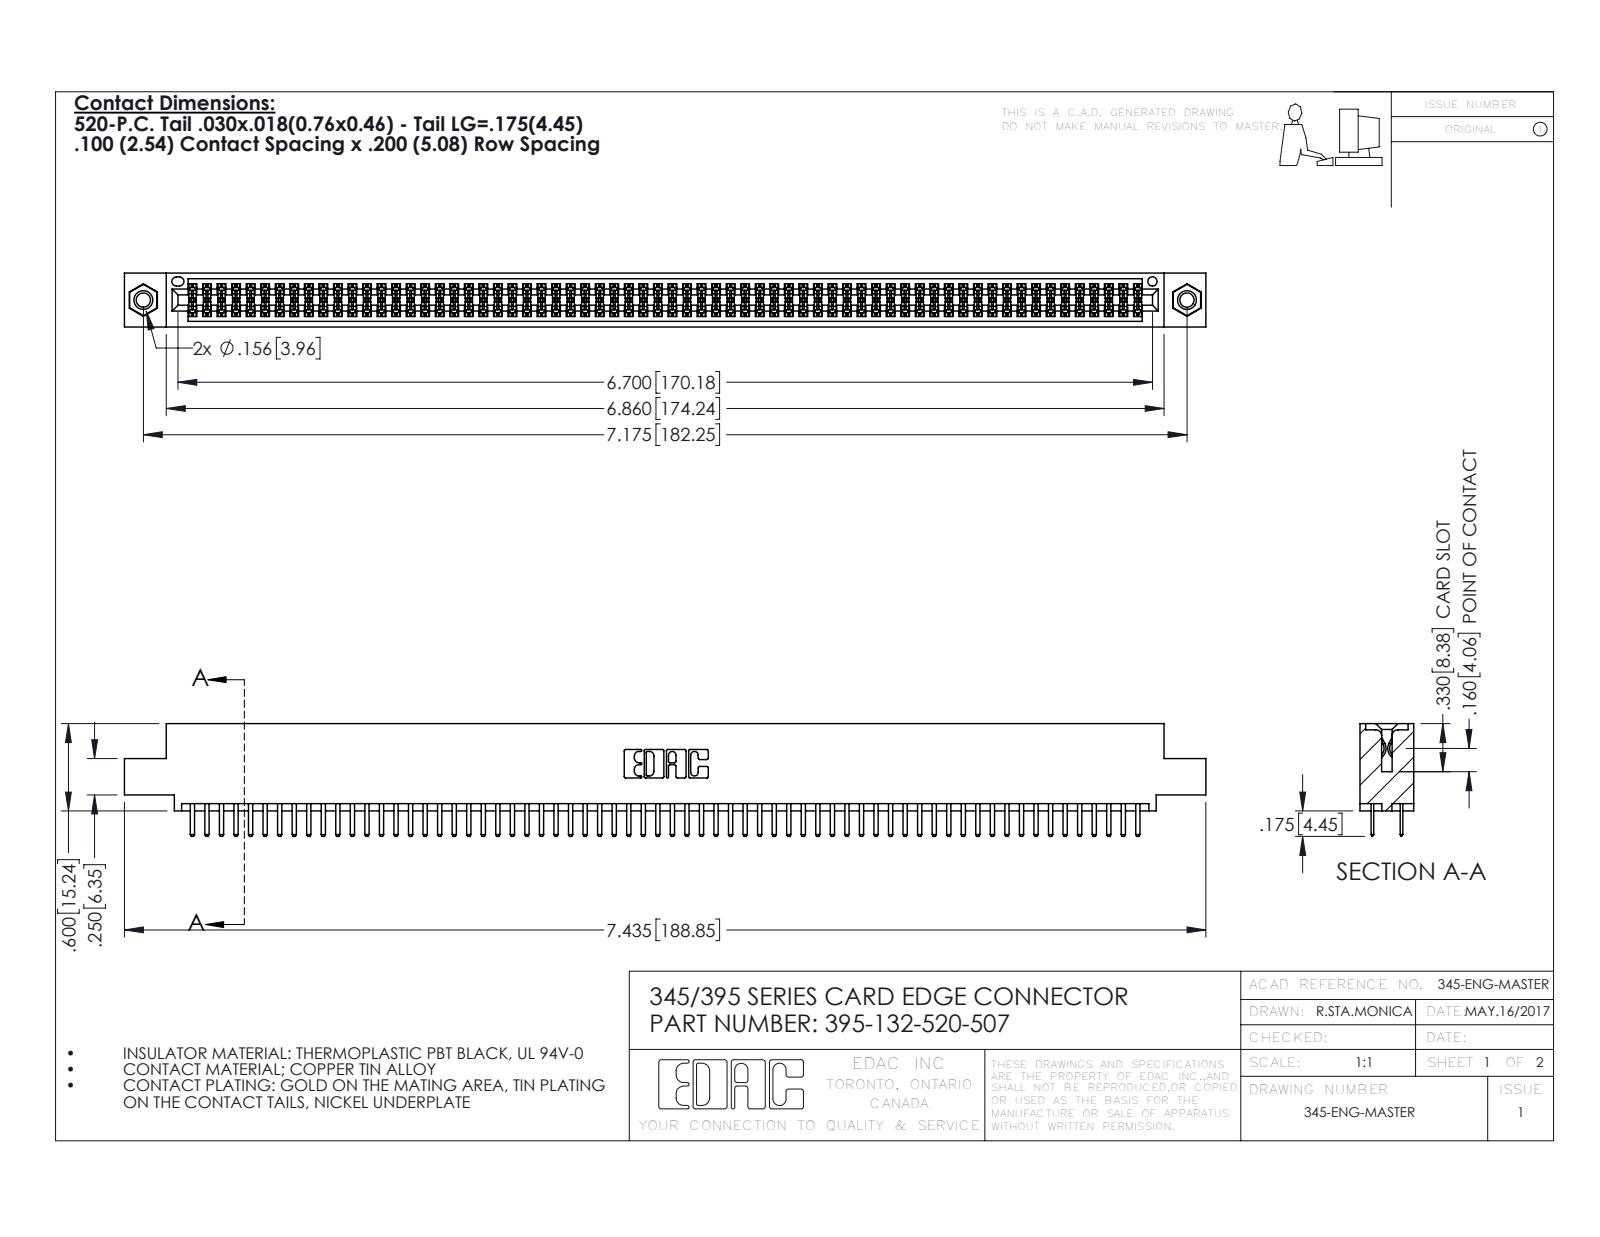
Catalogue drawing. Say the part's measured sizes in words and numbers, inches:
The part is named "345-292-001_345-293-120; 345-250-001_345-250-005-103; 345 Part_0.110 Offset - 0.156 Dia-TI; 395-132-520-507". Its 3-D file was written by "SolidWorks 2016 (CONFIG_CONTROL_DESIGN)". It is 135 solids with 7318 faces: 4736 planar, 2566 cylindrical and 16 other. Overall it measures 7.435 by 0.775 by 0.37 inches. Its volume is 1.124 cubic inches and its surface area 42.93 square inches. Round holes: 2 of diameter 0.098, 2 of diameter 0.125, 2 of diameter 0.156, 1 of diameter 0.064. Round bosses or shafts: 2 of diameter 0.155. Partial cylindrical surfaces (rounded edges, fillets, slot ends): 198 of radius 0.006, 136 of radius 0.01, 22 of radius 0.01, 6 of radius 0.007, 6 of radius 0.031, 3 of radius 0.026, 2 of radius 0.014, 2 of radius 0.019. The main face-to-face distances are 0.072, 0.298, 0.2, 0.37, 0.098, 0.272, 0.025, 0.225, 0.022, 0.072. The hole center spacings are 0.27, 6.939, 7.175.
